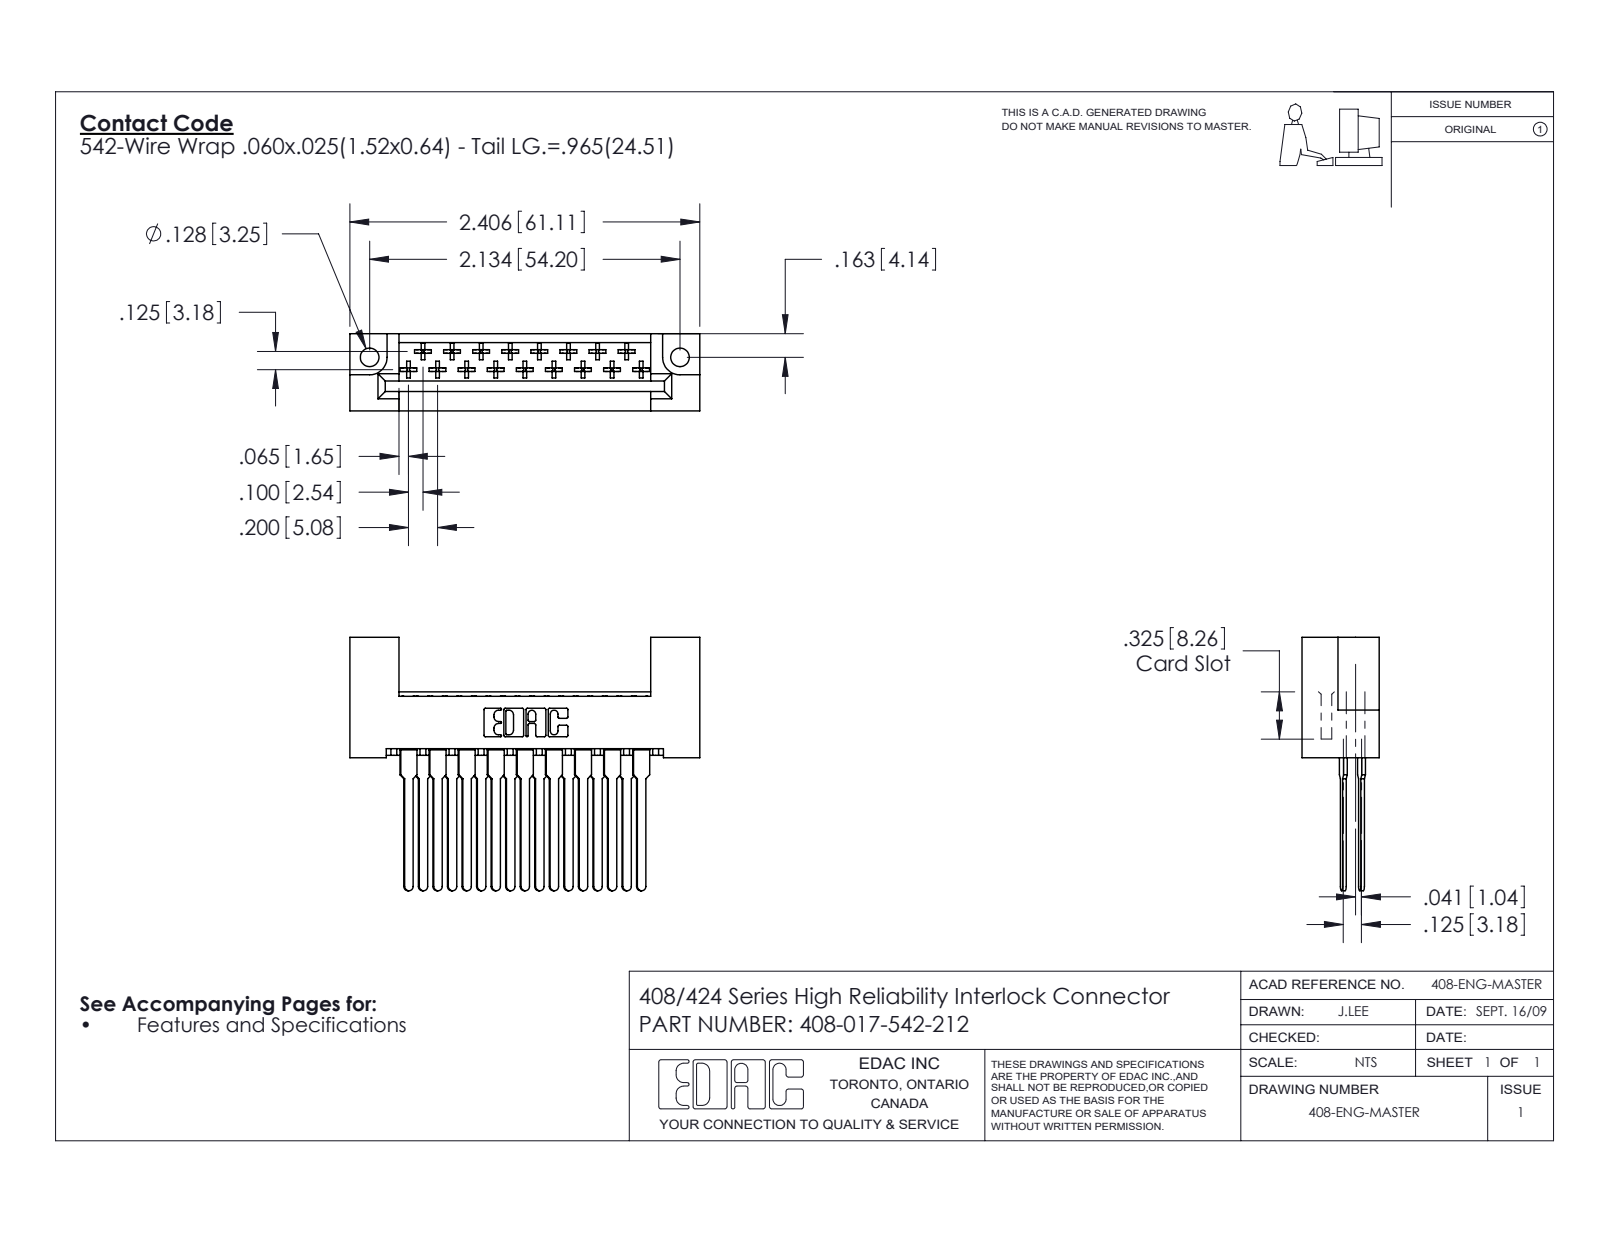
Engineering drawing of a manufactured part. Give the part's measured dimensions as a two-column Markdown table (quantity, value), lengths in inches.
| quantity | value |
| --- | --- |
| part name | 408-017-542-212; 408-290-001_408-290-142; 408 Part_017 - 2 |
| STEP written by | SolidWorks 2016 (CONFIG_CONTROL_DESIGN) |
| units | inches |
| bodies | 18 solids, 1040 faces (769 planar, 203 cylindrical, 68 other) |
| overall size | 2.406 × 1.742 × 0.531 |
| volume | 0.526 in³ |
| surface area | 16.02 in² |
| round holes (diameter × count) | 0.128 × 2 |
| partial cylindrical surfaces (radius × count) | 0.01 × 102, 0.01 × 22, 0.02 × 19, 0.03 × 17, 0.007 × 6, 0.031 × 6, 0.026 × 3, 0.12 × 2 |
| main face-to-face distances | 0.531, 0.025, 0.104, 0.125, 0.095, 0.025, 0.1, 0.133, 0.361, 0.326 |
| hole center spacings | 2.134 |
